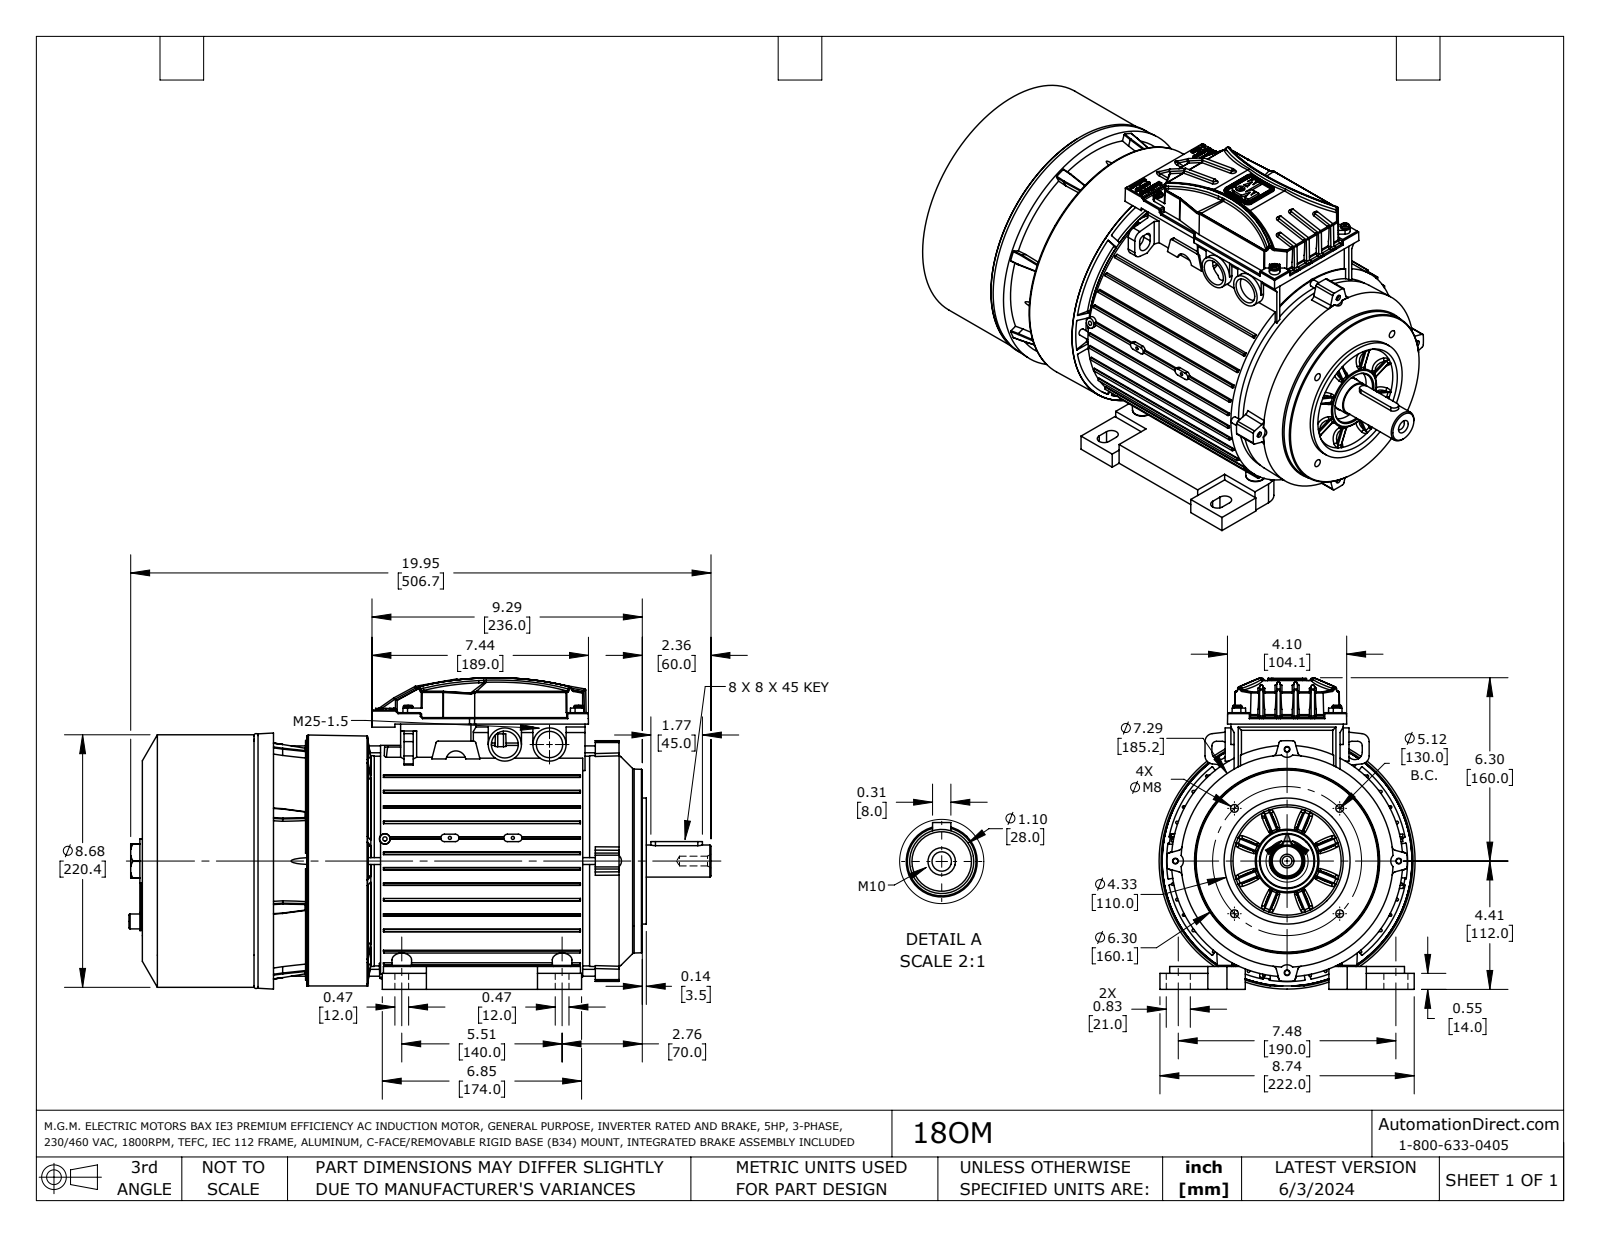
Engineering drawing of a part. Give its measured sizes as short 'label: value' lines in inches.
name: 18OM
written by: SolidWorks 2021 (AUTOMOTIVE_DESIGN)
unit: in
bodies: 12 solids, 3436 faces (1289 planar, 733 cylindrical, 1414 other)
size: 20.007 × 10.709 × 8.799
volume: 853.2 in³; area: 1 248 in²
holes: 11× ⌀0.13, 5× ⌀0.098, 5× ⌀0.335, 4× ⌀0.15, 4× ⌀0.177, 4× ⌀0.197, 4× ⌀0.268, 4× ⌀0.531, 3× ⌀0.148, 3× ⌀0.165, 2× ⌀0.106, 2× ⌀0.118
bosses: 8× ⌀0.315, 6× ⌀0.138, 4× ⌀0.522, 4× ⌀0.236, 2× ⌀1.142, 1× ⌀8.677, 1× ⌀8.563, 1× ⌀7.951
rounds: 66× R0.039, 56× R0.008, 47× R0.059, 30× R0.079, 24× R0.004, 22× R0.02, 16× R0.033, 12× R0.276
face distances: 15.374, 0.787, 0.236, 1.811, 17.185, 8.445, 0.106, 9.45, 7.639, 7.735
hole spacings: 0.472, 2.719, 5.931, 0.818, 2.25, 2.106, 2.479, 2.559
